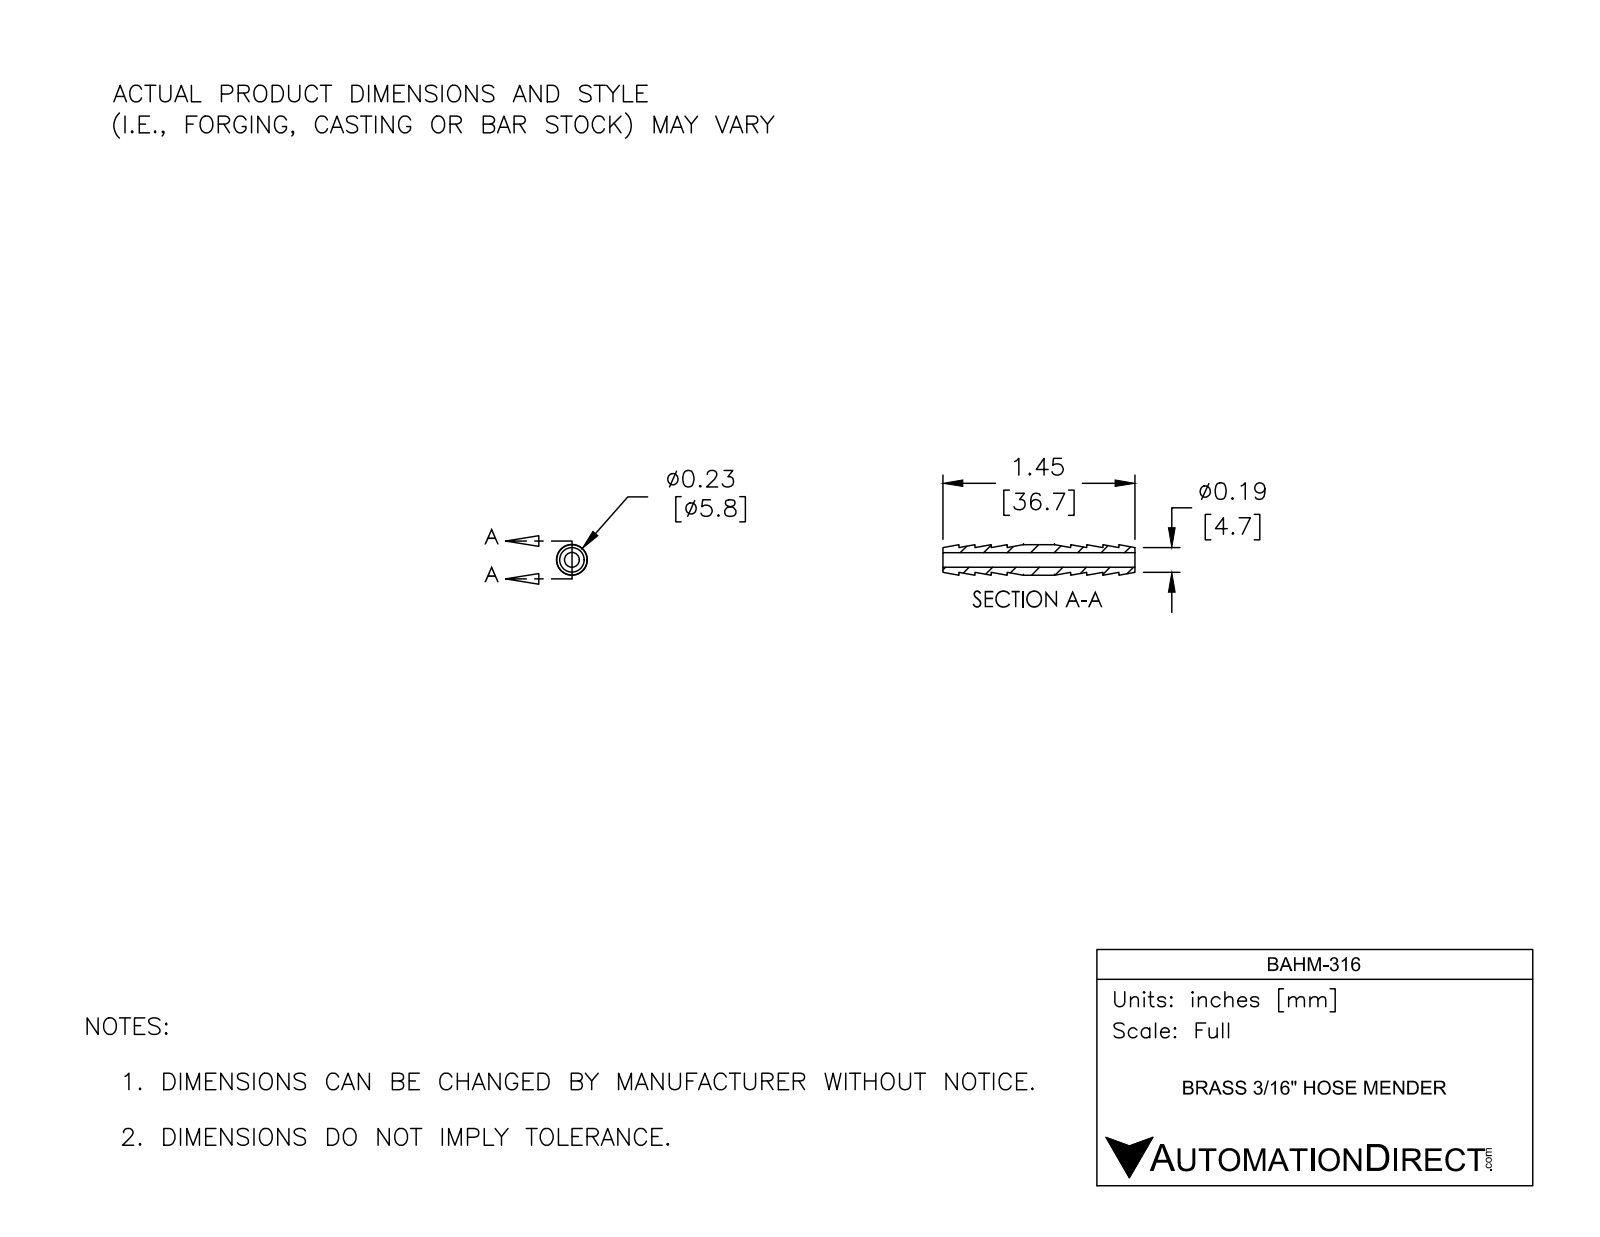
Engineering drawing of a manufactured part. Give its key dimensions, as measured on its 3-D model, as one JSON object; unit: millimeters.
{"part_name": "BAHM-316", "step_written_by": "SolidWorks 2017 (AUTOMOTIVE_DESIGN)", "units": "millimeters", "bodies": {"solids": 1, "faces": 40, "planar": 12, "cylindrical": 8, "other": 20}, "overall_size": [36.7, 5.8, 5.8], "volume_mm3": 610, "surface_area_mm2": 1045, "round_holes": [[2.8, 1]], "round_bosses_or_shafts": [[5.8, 1], [5.8, 1]], "face_to_face_distances": [3.1, 9.2, 6.1, 24.4, 21.4, 30.6, 6.1, 12.3, 27.5, 33.7]}
